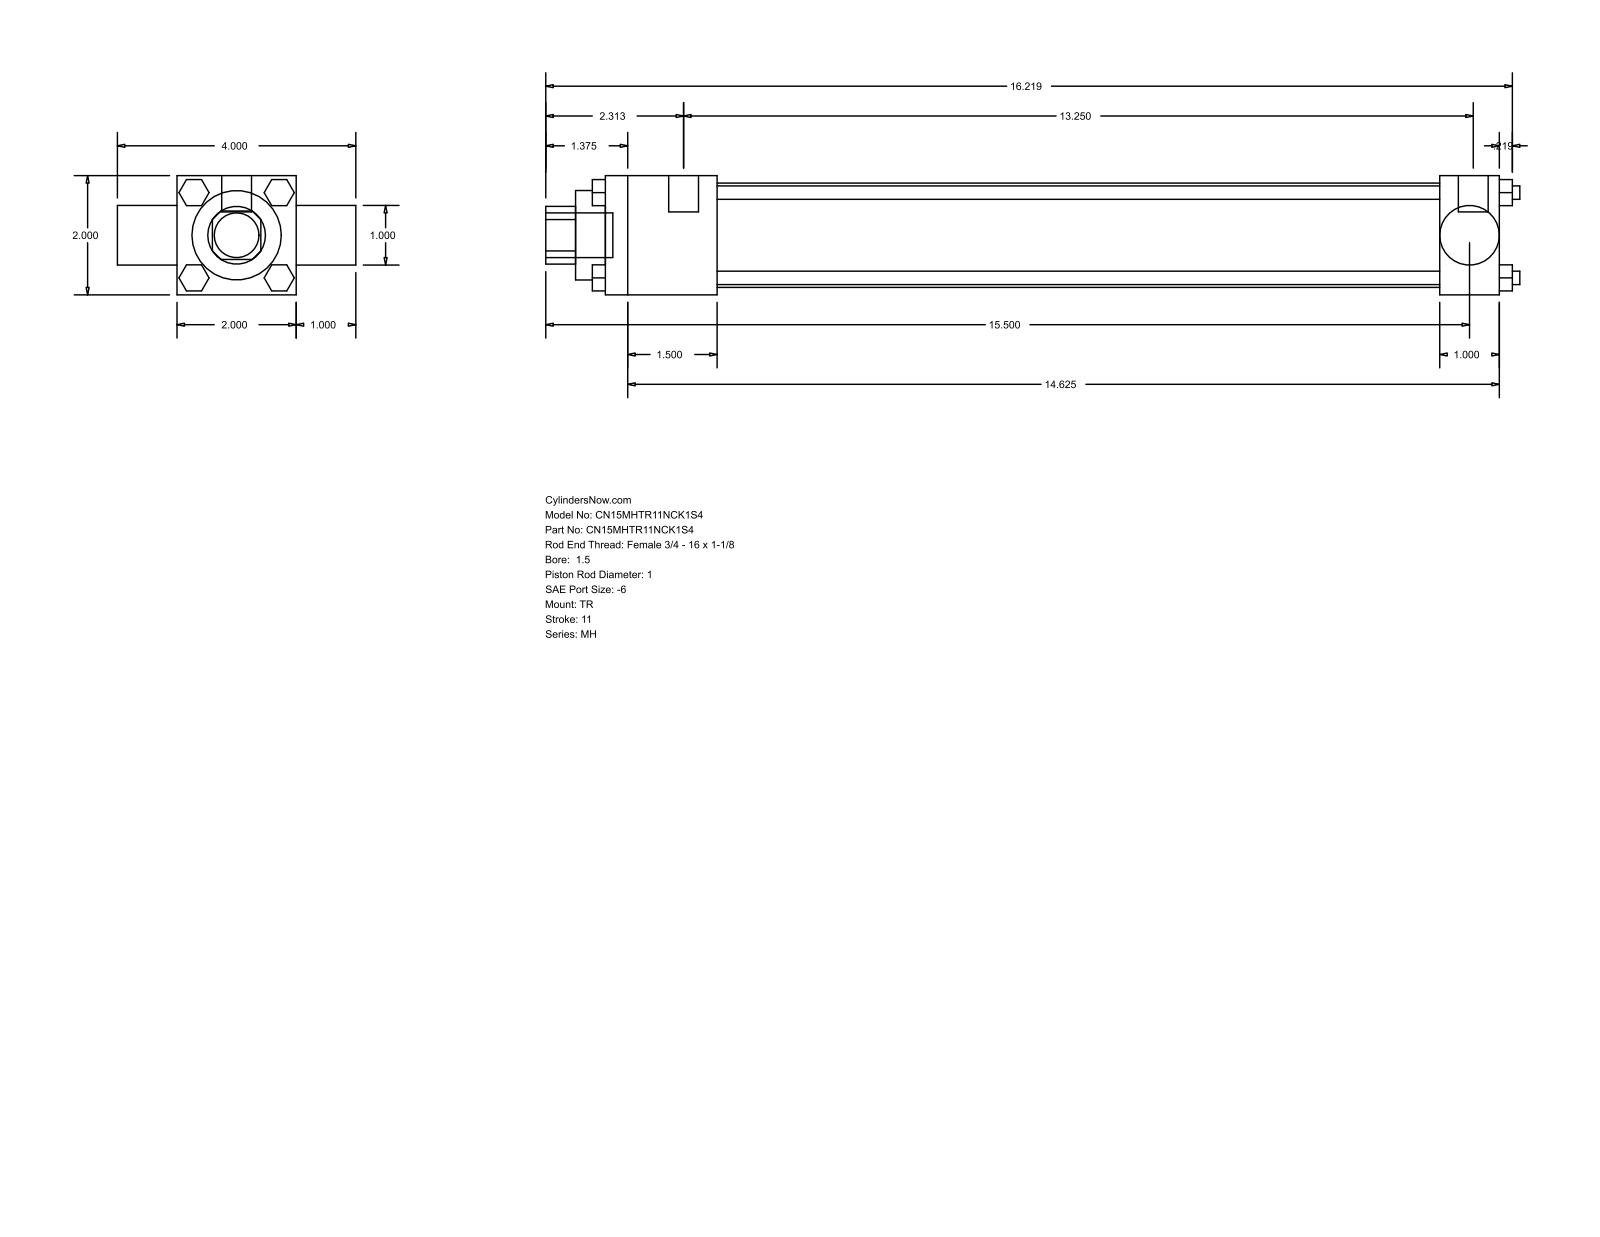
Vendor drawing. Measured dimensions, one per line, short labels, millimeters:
name: MH_TR__0150_1
written by: GSSL Pune (CONFIG_CONTROL_DESIGN)
unit: mm
bodies: 0 solids, 120 faces (92 planar, 28 cylindrical, 0 other)
size: 415.13 × 101.6 × 50.8
holes: 1× ⌀25.35, 1× ⌀25.4, 1× ⌀38.1, 1× ⌀44.45
bosses: 4× ⌀5.71, 3× ⌀5.56, 2× ⌀12.7, 1× ⌀19.05
rounds: 1× R12.29
face distances: 50.8, 25.4, 381, 76.2, 47.63, 333.37, 355.6, 307.97, 386.56, 12.7
